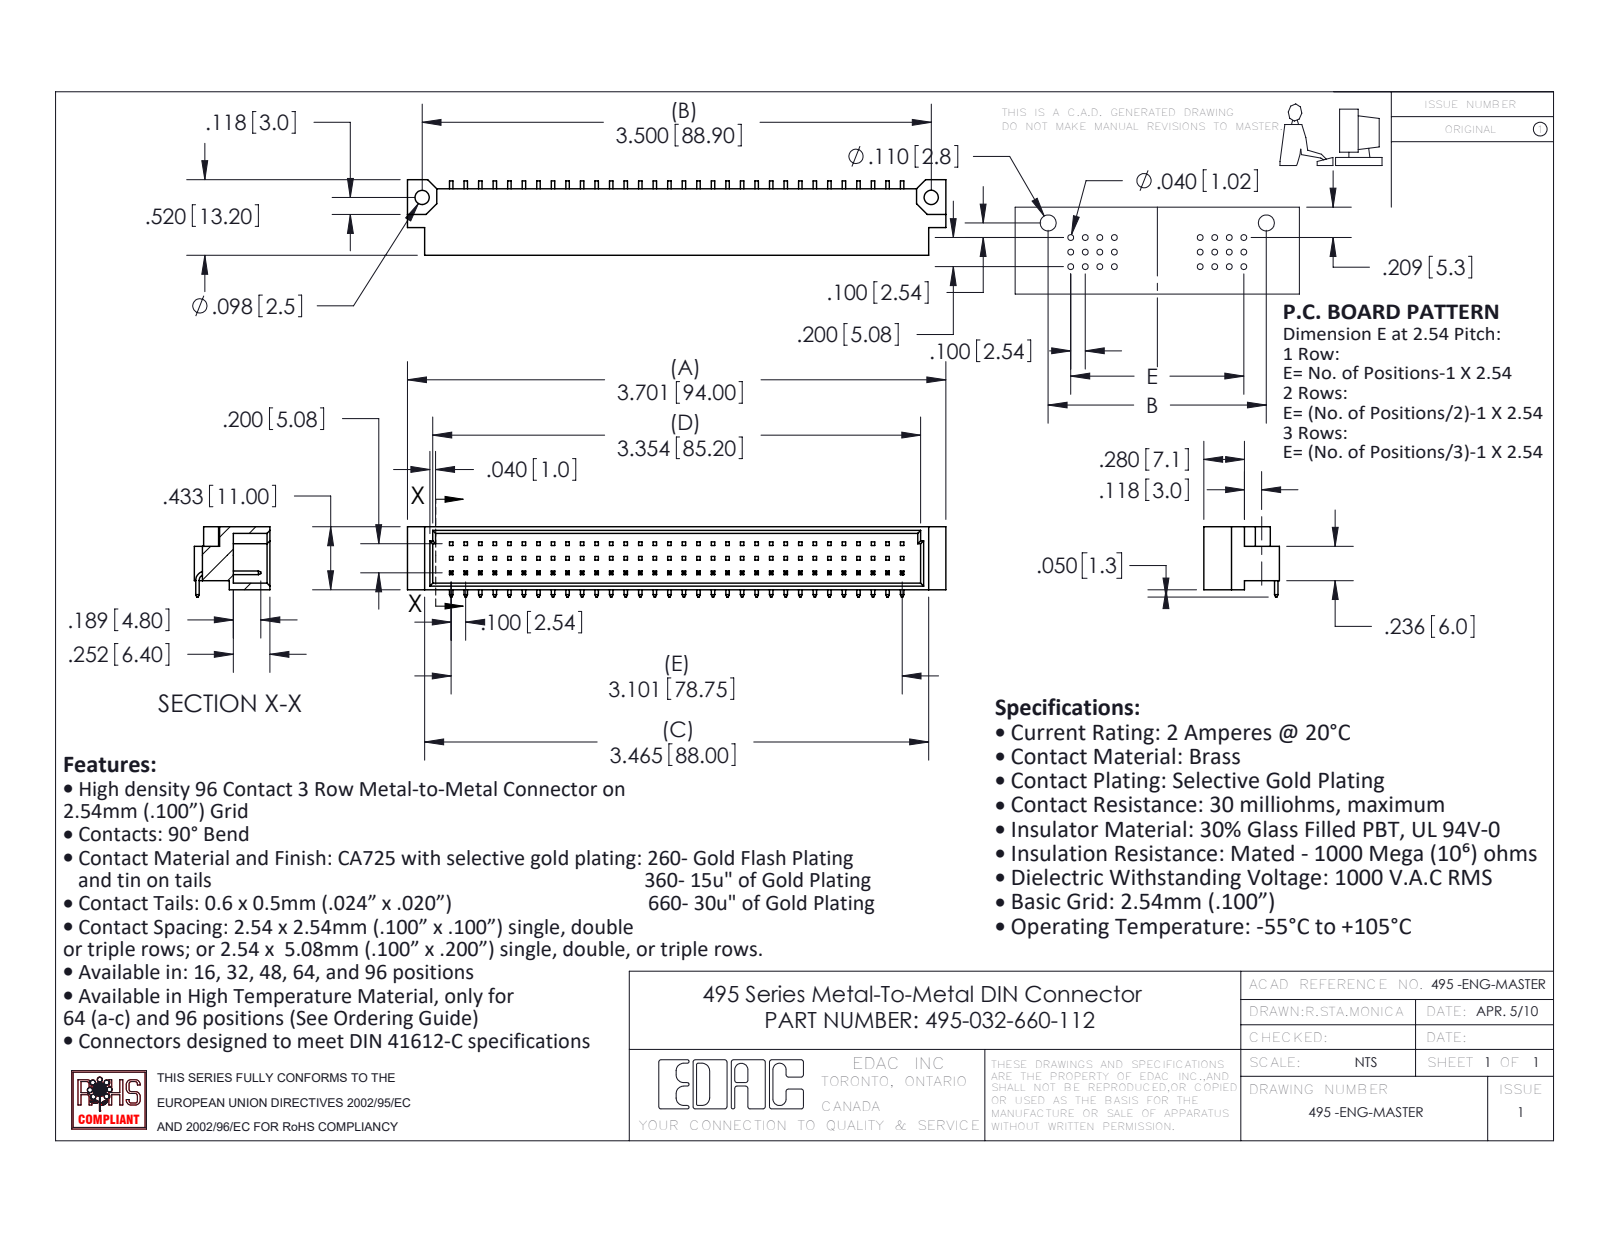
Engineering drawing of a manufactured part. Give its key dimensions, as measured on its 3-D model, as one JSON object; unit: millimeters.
{"part_name": "495 Part_96; 495-290-3; 495-032-660-112", "step_written_by": "SolidWorks 2020 (AUTOMOTIVE_DESIGN)", "units": "millimeters", "bodies": {"solids": 33, "faces": 1009, "planar": 941, "cylindrical": 68, "other": 0}, "overall_size": [94, 13.2, 12.27], "volume_mm3": 6100, "surface_area_mm2": 7981, "round_holes": [[2.49, 2]], "partial_cylinders_radius": [[1.02, 1], [1.65, 1]], "face_to_face_distances": [1.14, 9.86, 5.2, 11, 2.54, 0.61, 8.72, 1.6, 9.4, 0.46], "hole_center_spacings": [88.9]}
